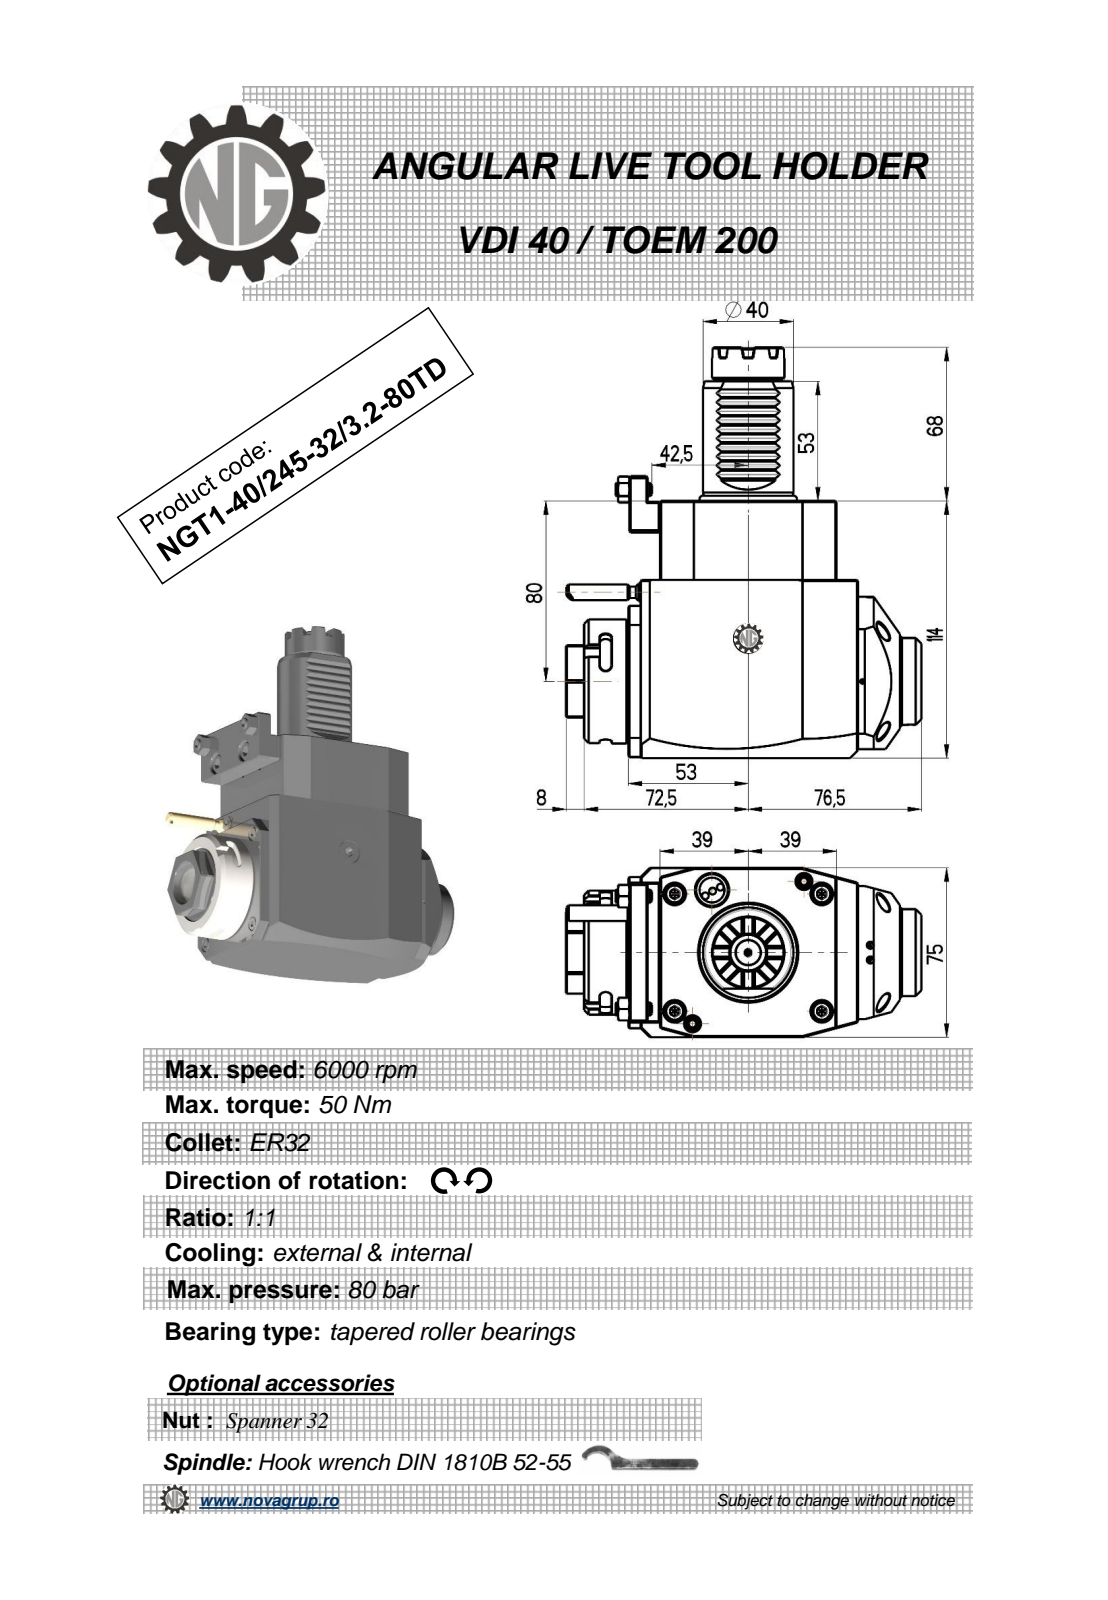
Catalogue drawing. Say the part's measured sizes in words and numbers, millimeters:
The part is named "NGT1_40_245_32_3_2_80TD". Its 3-D file was written by "PRO/ENGINEER BY PARAMETRIC TECHNOLOGY CORPORATION, 2010280 (CONFIG_CONTROL_DESIGN)". It is 1 solid with 425 faces: 225 planar, 68 cylindrical and 132 other. Overall it measures 182 by 157 by 75 millimeters. Its volume is 980 713 cubic millimeters and its surface area 74 303 square millimeters. Round holes: 1 of diameter 2.5, 1 of diameter 3, 1 of diameter 23. Round bosses or shafts: 2 of diameter 6, 1 of diameter 55, 1 of diameter 48, 1 of diameter 40, 1 of diameter 38.5, 1 of diameter 32, 1 of diameter 17.2, 1 of diameter 8. Partial cylindrical surfaces (rounded edges, fillets, slot ends): 10 of radius 0.3, 10 of radius 0.31, 6 of radius 2.5, 2 of radius 180, 1 of radius 0.5, 1 of radius 24.5, 1 of radius 37.5. The main face-to-face distances are 75, 114, 0.5, 14, 92, 121, 28, 13.5, 19.5, 111.5. The hole center spacings are 43.2.
